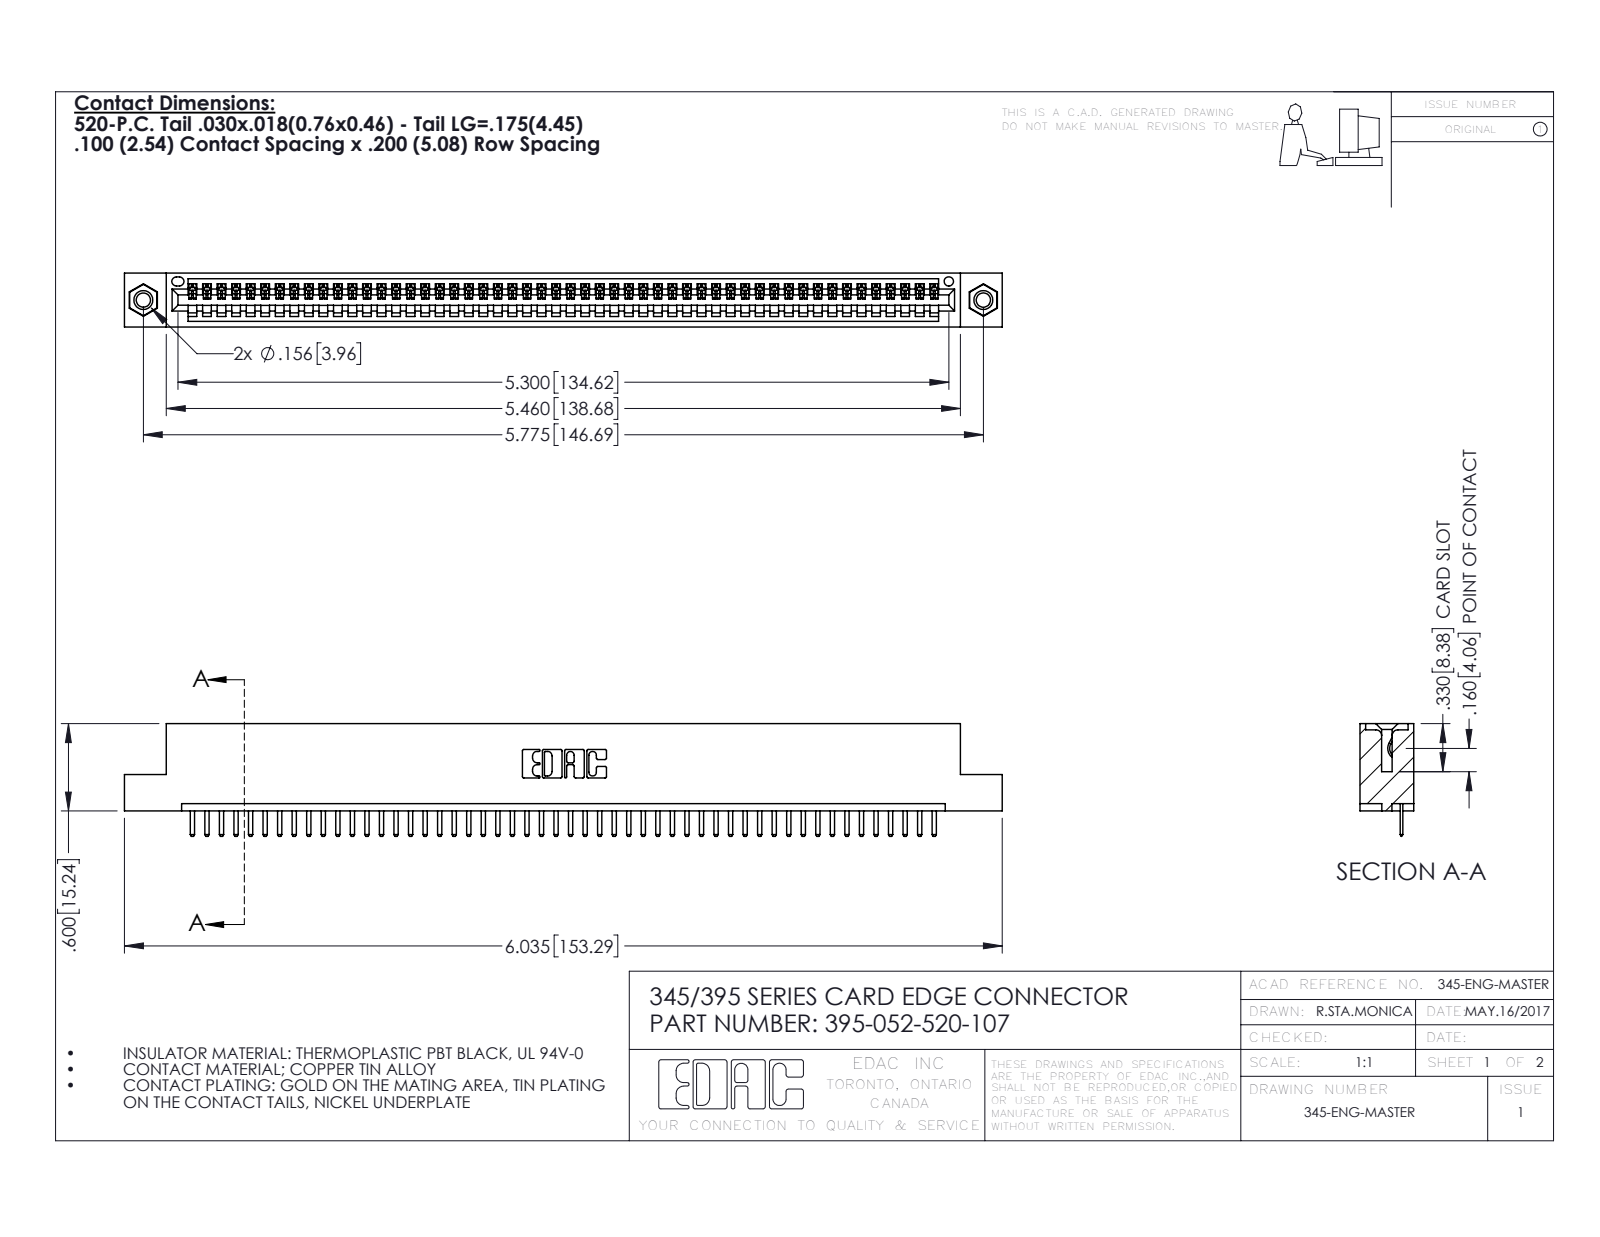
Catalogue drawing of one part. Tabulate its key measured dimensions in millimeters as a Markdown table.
| quantity | value |
| --- | --- |
| part name | 395-052-520-107; 345 Part_Flush Mounting Lugs - 0.156 Dia-TI; 345-292-001_345-293-120; 345-250-001_345-250-005-103 |
| STEP written by | SolidWorks 2016 (CONFIG_CONTROL_DESIGN) |
| units | millimeters |
| bodies | 55 solids, 3410 faces (2296 planar, 1098 cylindrical, 16 other) |
| overall size | 153.3 × 19.7 × 9.4 |
| volume | 14 500 mm³ |
| surface area | 18 920 mm² |
| round holes (diameter × count) | 2.5 × 2, 3.2 × 2, 4 × 2, 1.6 × 1 |
| round bosses / shafts (diameter × count) | 3.9 × 2 |
| partial cylindrical surfaces (radius × count) | 0.3 × 106, 0.2 × 104, 0.3 × 22, 0.2 × 6, 0.8 × 6, 0.7 × 3, 0.8 × 2, 1 × 2 |
| main face-to-face distances | 1.8, 7.6, 9.4, 5.1, 2.5, 6.9, 0.6, 5.7, 1.8, 3.8 |
| hole center spacings | 6.9, 140.7, 146.7 |
